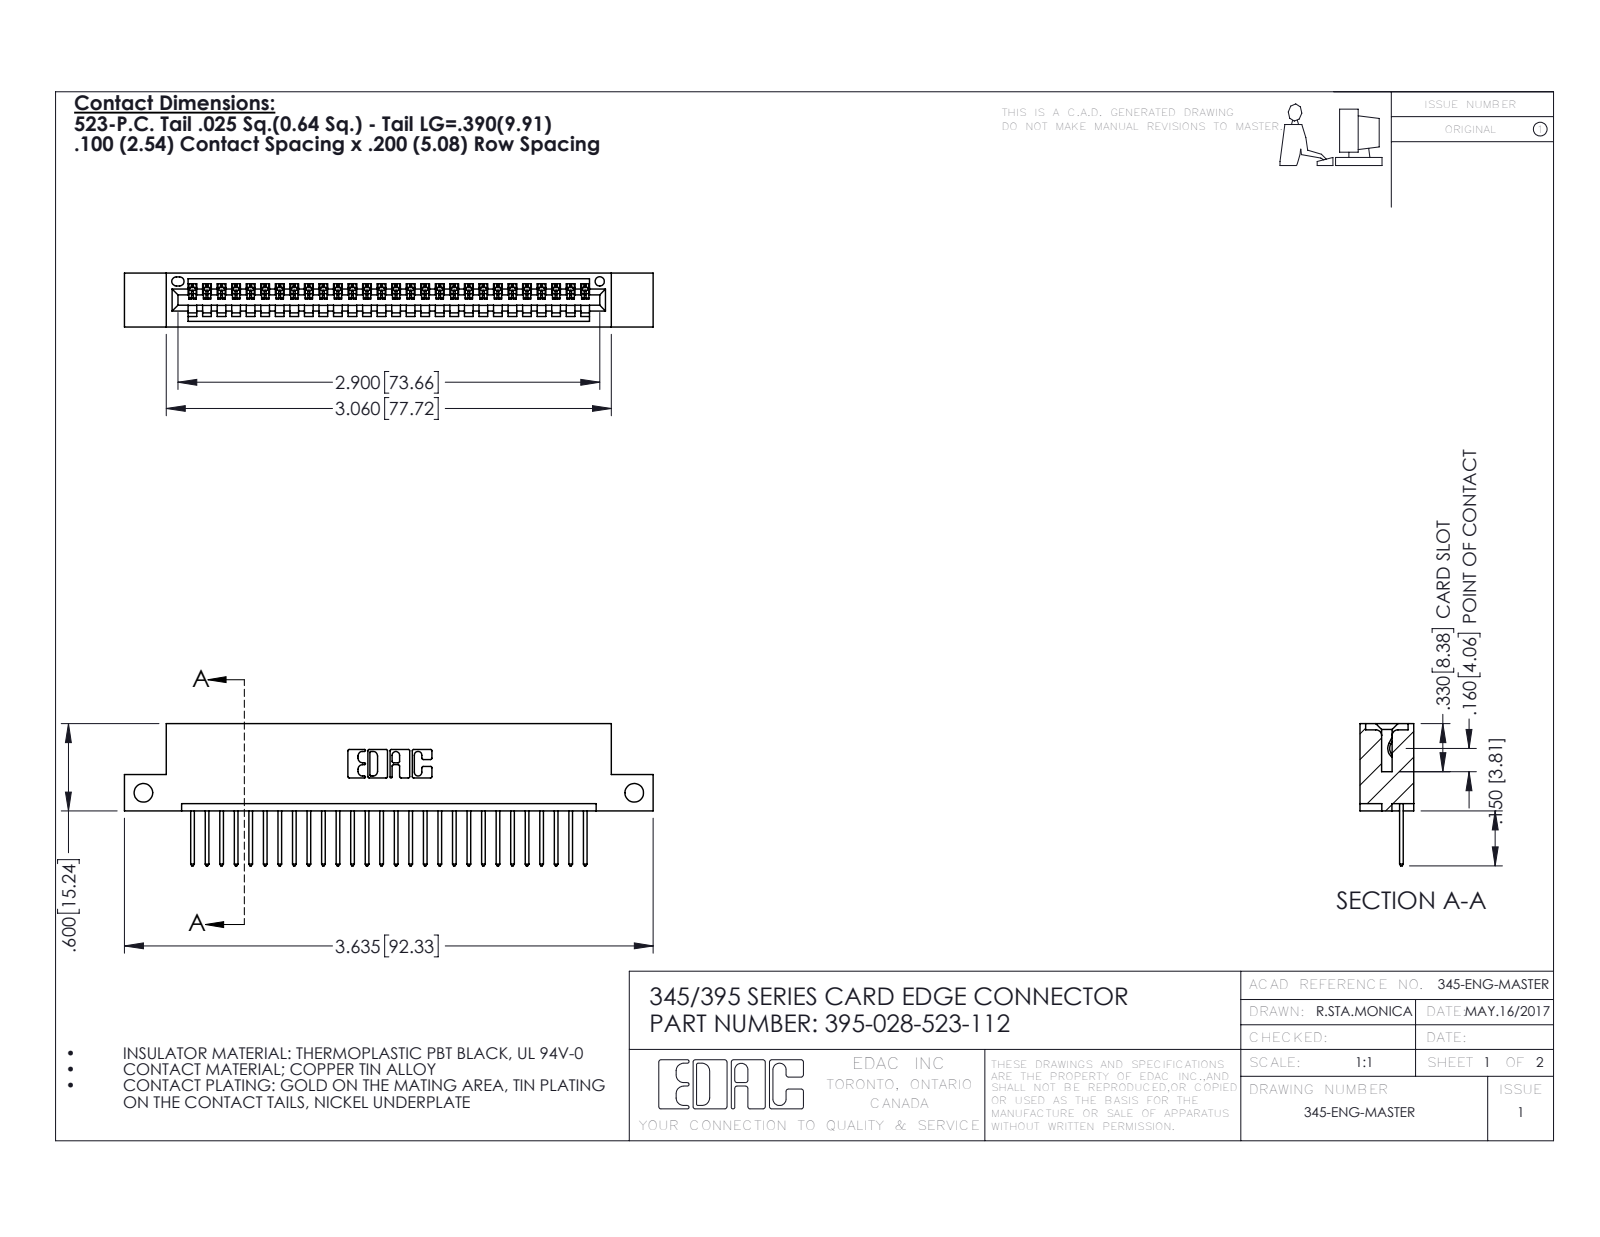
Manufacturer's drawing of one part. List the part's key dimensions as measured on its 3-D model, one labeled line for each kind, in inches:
Part name (STEP PRODUCT): 395-028-523-112; 345-292-001_345-293-123; 345 Part_Flush Mounting Lugs - Side Mount
STEP written by: SolidWorks 2016 (CONFIG_CONTROL_DESIGN)
Units: inches
Bodies: 29 solids, 1750 faces (1200 planar, 550 cylindrical, 0 other)
Overall size (bounding box): 3.635 × 0.977 × 0.37
Volume: 0.522 in³ · Surface area: 17.16 in²
Round holes (diameter × count): ⌀0.128 ×2, ⌀0.064 ×1
Partial cylindrical surfaces — rounded edges, fillets, slot ends (radius × count): R0.006 ×56, R0.01 ×56, R0.01 ×22, R0.007 ×6, R0.031 ×6, R0.026 ×3, R0.031 ×2, R0.04 ×2
Main face-to-face distances: 0.298, 0.072, 0.2, 0.37, 0.098, 0.272, 0.025, 0.225, 0.149, 0.072
Hole centre spacings: 3.375
